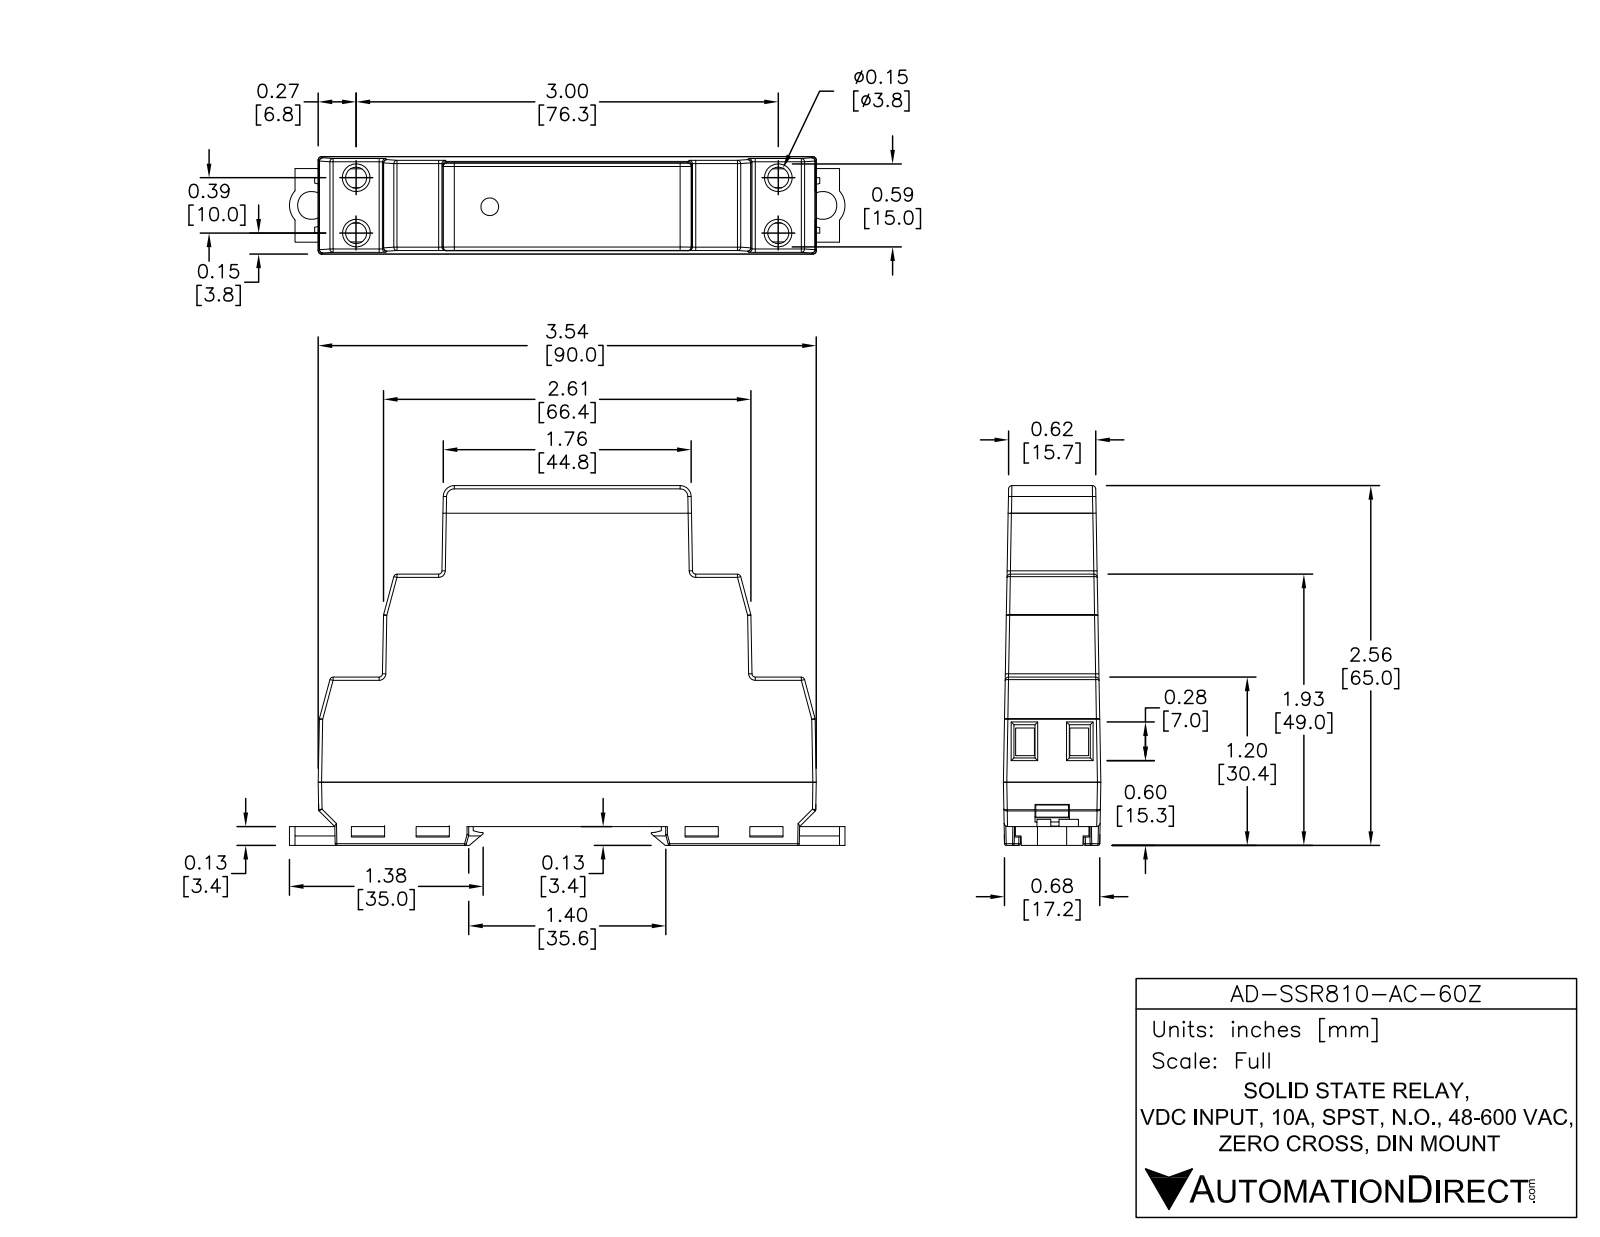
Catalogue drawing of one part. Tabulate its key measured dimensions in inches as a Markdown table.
| quantity | value |
| --- | --- |
| part name | AD-SSR810-AC-60Z |
| STEP written by | SolidWorks 2013 (AUTOMOTIVE_DESIGN) |
| units | inches |
| bodies | 1 solid, 832 faces (491 planar, 78 cylindrical, 263 other) |
| overall size | 3.924 × 2.616 × 0.685 |
| volume | 4.605 in³ |
| surface area | 24.23 in² |
| round holes (diameter × count) | 0.19 × 4, 0.2 × 2 |
| round bosses / shafts (diameter × count) | 0.105 × 1 |
| partial cylindrical surfaces (radius × count) | 0.015 × 41, 0.06 × 2, 0.172 × 2 |
| main face-to-face distances | 2.525, 0.049, 2.574, 0.425, 2.215, 0.025, 0.05, 1.934, 1.885, 0.64 |
| hole center spacings | 0.338, 3.3, 0.364, 3.01, 3.032, 3.58 |
